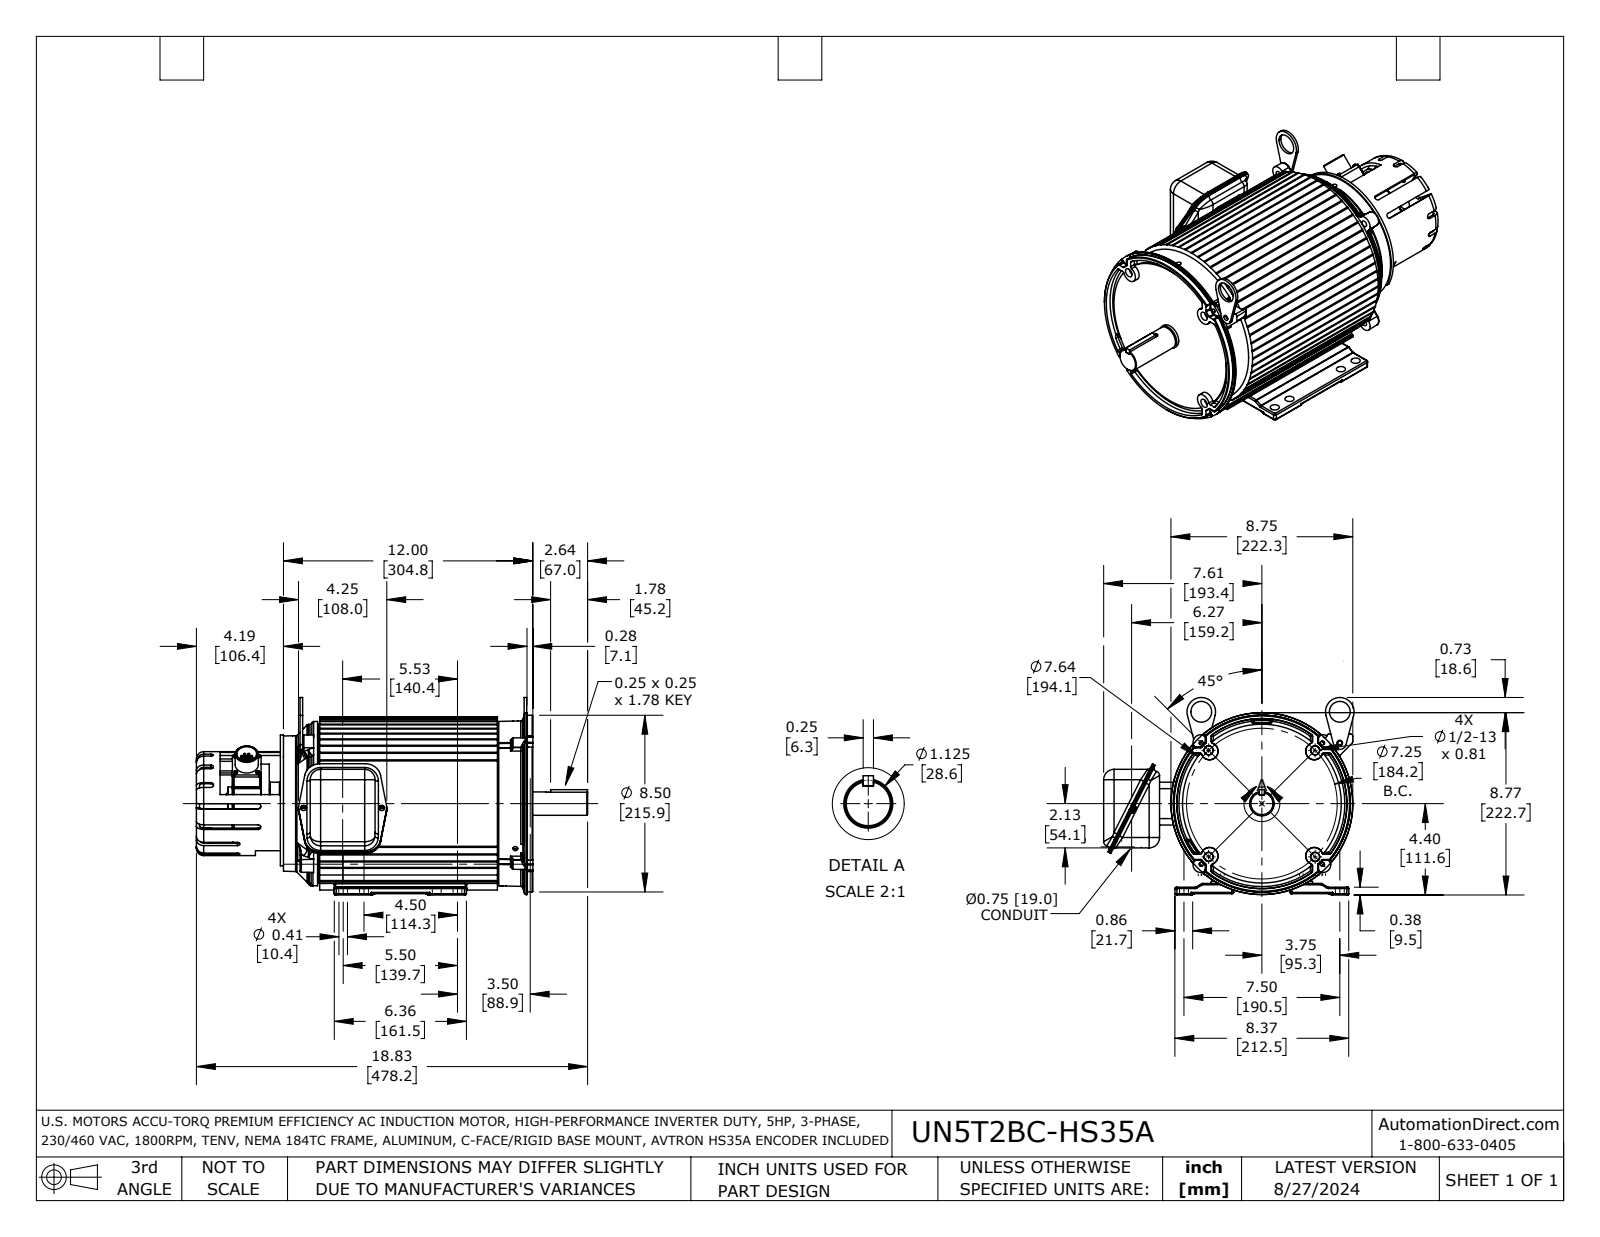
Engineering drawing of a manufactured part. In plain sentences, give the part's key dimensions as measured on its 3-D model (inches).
The part is named "UN5T2BC-HS35A". Its 3-D file was written by "SolidWorks 2021 (AUTOMOTIVE_DESIGN)". It is 22 solids with 2945 faces: 716 planar, 781 cylindrical and 1448 other. Overall it measures 18.826 by 12.052 by 9.5 inches. Its volume is 658 cubic inches and its surface area 1 131 square inches. Round holes: 6 of diameter 0.4, 4 of diameter 0.12, 4 of diameter 0.2, 4 of diameter 0.234, 4 of diameter 0.277, 3 of diameter 0.136, 3 of diameter 1, 2 of diameter 0.232, 2 of diameter 0.266, 2 of diameter 0.281, 1 of diameter 0.174, 1 of diameter 0.5. Round bosses or shafts: 8 of diameter 0.072, 4 of diameter 0.175, 4 of diameter 0.12, 3 of diameter 0.15, 2 of diameter 0.328, 2 of diameter 0.072, 1 of diameter 8.5, 1 of diameter 8.315. Partial cylindrical surfaces (rounded edges, fillets, slot ends): 140 of radius 0.063, 52 of radius 0.061, 48 of radius 0.031, 37 of radius 0.125, 22 of radius 0.06, 20 of radius 0.094, 14 of radius 0.5, 10 of radius 0.16. The main face-to-face distances are 12.831, 2.033, 10.798, 1.08, 0.953, 11.752, 1.375, 2.455, 3.408, 14.206. The hole center spacings are 2.073, 3.387, 4.319, 1.5, 2.22, 0.754, 1.75, 2.475.
